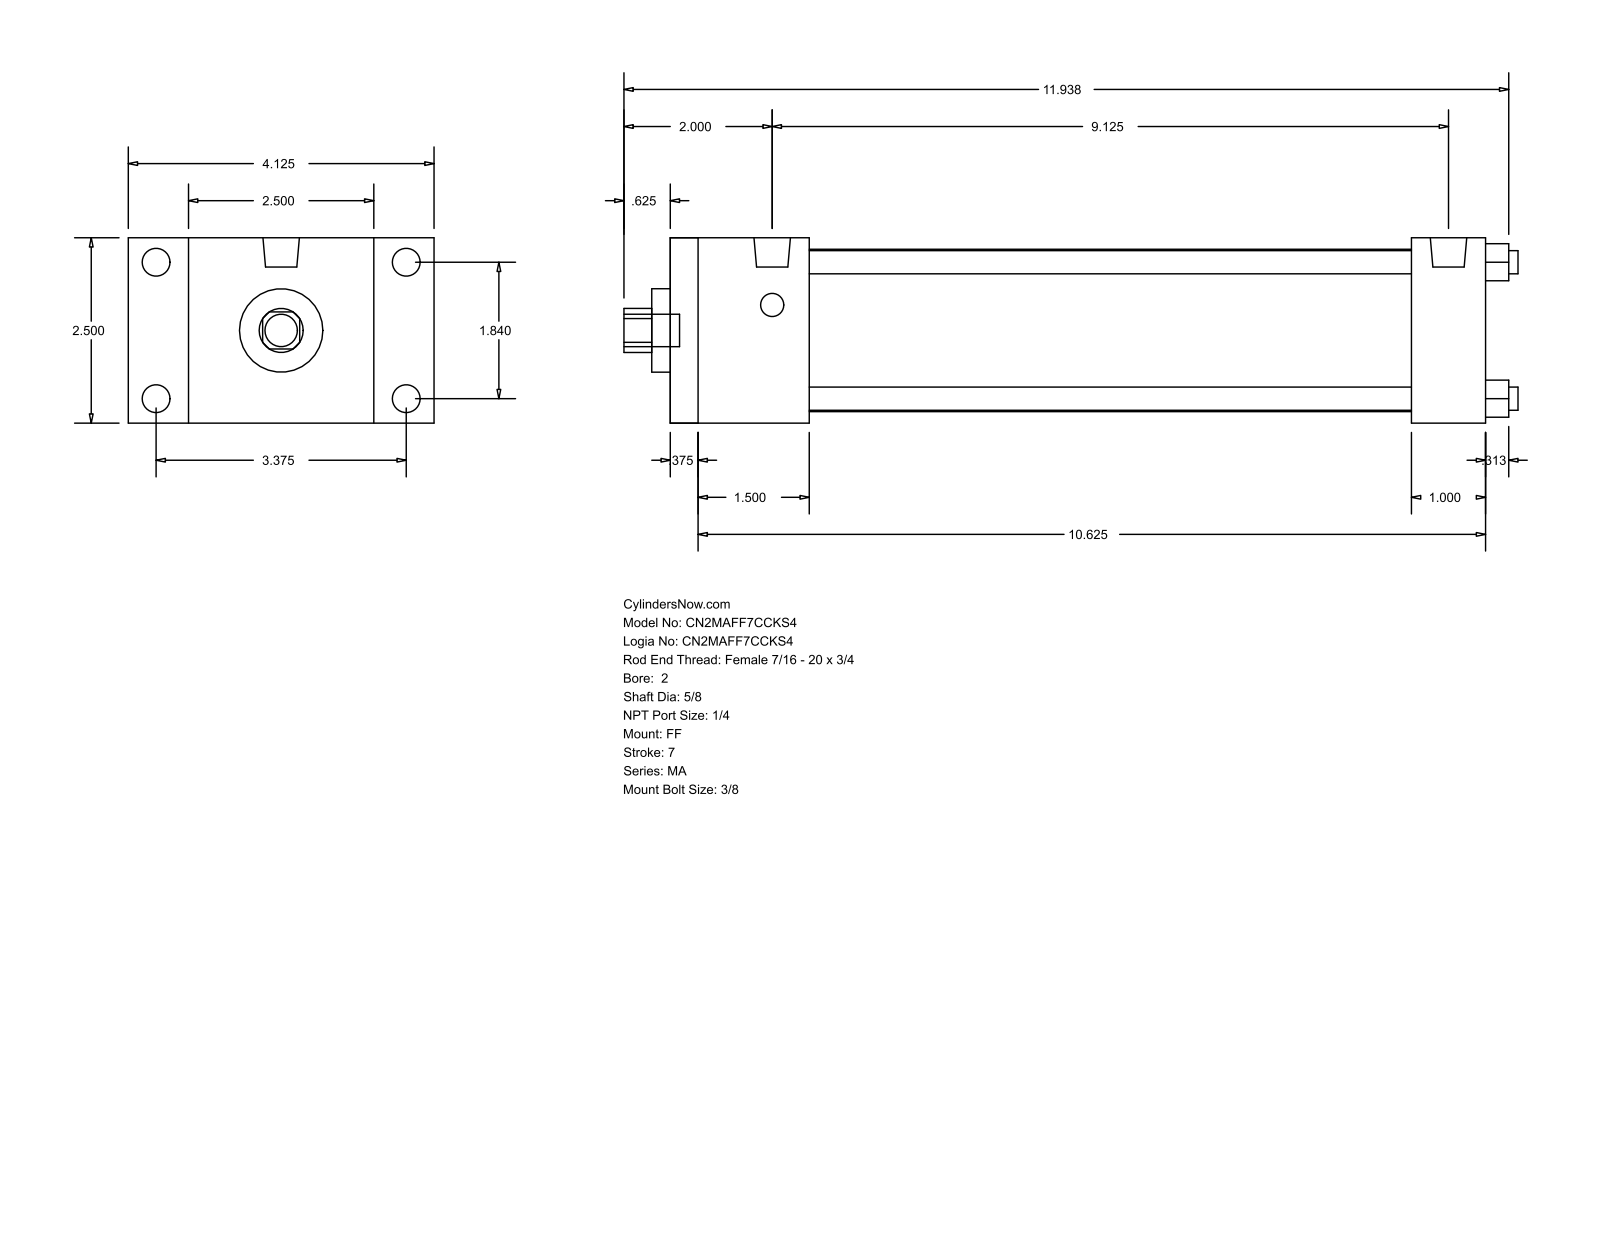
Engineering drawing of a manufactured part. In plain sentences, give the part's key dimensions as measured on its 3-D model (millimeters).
The part is named "MA_FF__0200_0.625". Its 3-D file was written by "GSSL Pune (CONFIG_CONTROL_DESIGN)". It is 0 solids with 92 faces: 64 planar, 28 cylindrical and 0 other. Overall it measures 306.39 by 104.78 by 63.5 millimeters. Round holes: 4 of diameter 7.94, 1 of diameter 15.88, 1 of diameter 28.57, 1 of diameter 55.63. Round bosses or shafts: 4 of diameter 9.53, 4 of diameter 7.94, 2 of diameter 12.49, 1 of diameter 11.11. Partial cylindrical surfaces (rounded edges, fillets, slot ends): 1 of radius 7.54. The main face-to-face distances are 63.5, 279.39, 9.52, 269.87, 38.1, 47.62, 254, 244.48, 206.38, 231.77. The hole center spacings are 33.05, 46.74, 66.1.
